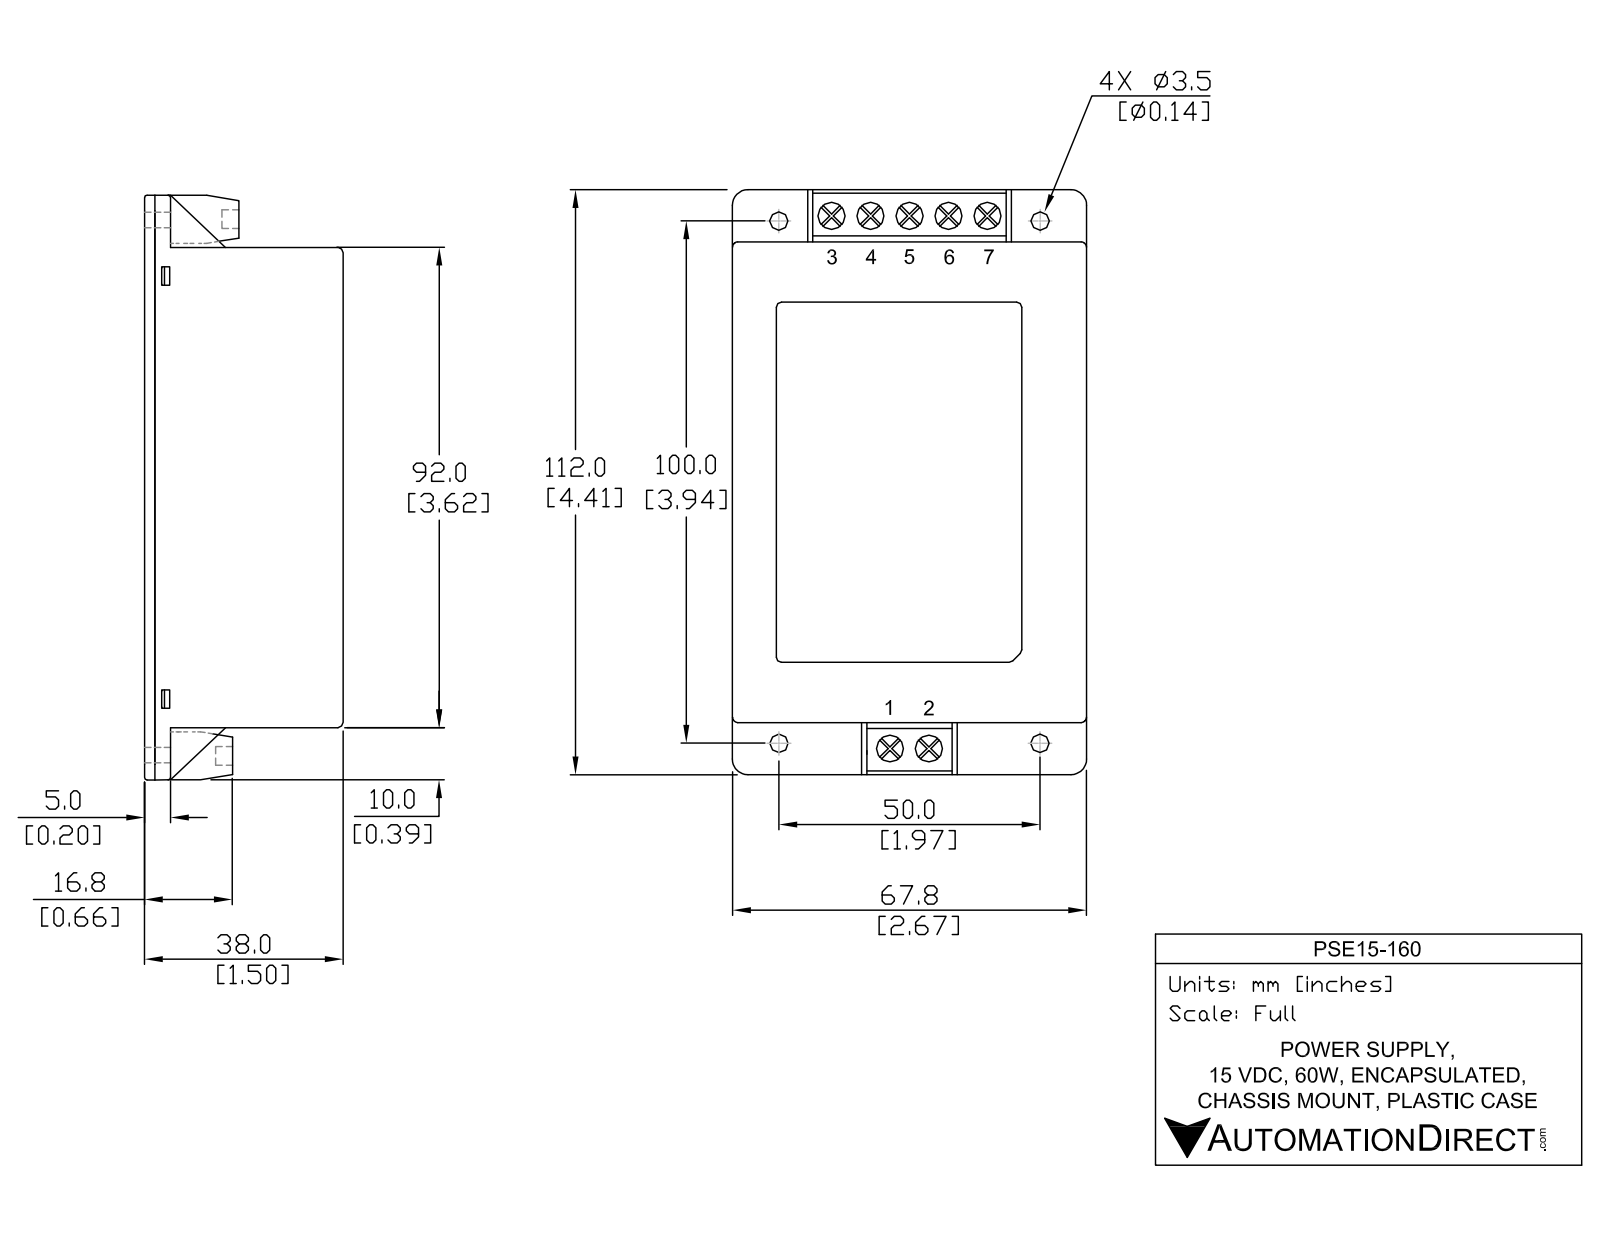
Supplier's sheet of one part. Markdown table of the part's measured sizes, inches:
| quantity | value |
| --- | --- |
| part name | PSE15-160 |
| STEP written by | SolidWorks 2011 (CONFIG_CONTROL_DESIGN) |
| units | inches |
| bodies | 2 solids, 374 faces (246 planar, 62 cylindrical, 66 other) |
| overall size | 4.41 × 2.67 × 1.5 |
| volume | 15.18 in³ |
| surface area | 69.77 in² |
| round holes (diameter × count) | 0.2 × 7, 0.14 × 4 |
| partial cylindrical surfaces (radius × count) | 0.03 × 20, 0.125 × 4 |
| main face-to-face distances | 0.078, 0.08, 1.42, 2.67, 1.498, 1.418, 1.5, 1.422, 3.62, 0.015 |
| hole center spacings | 0.26, 0.52, 0.26, 0.856, 1.116, 1.97, 3.94, 4.015 |
